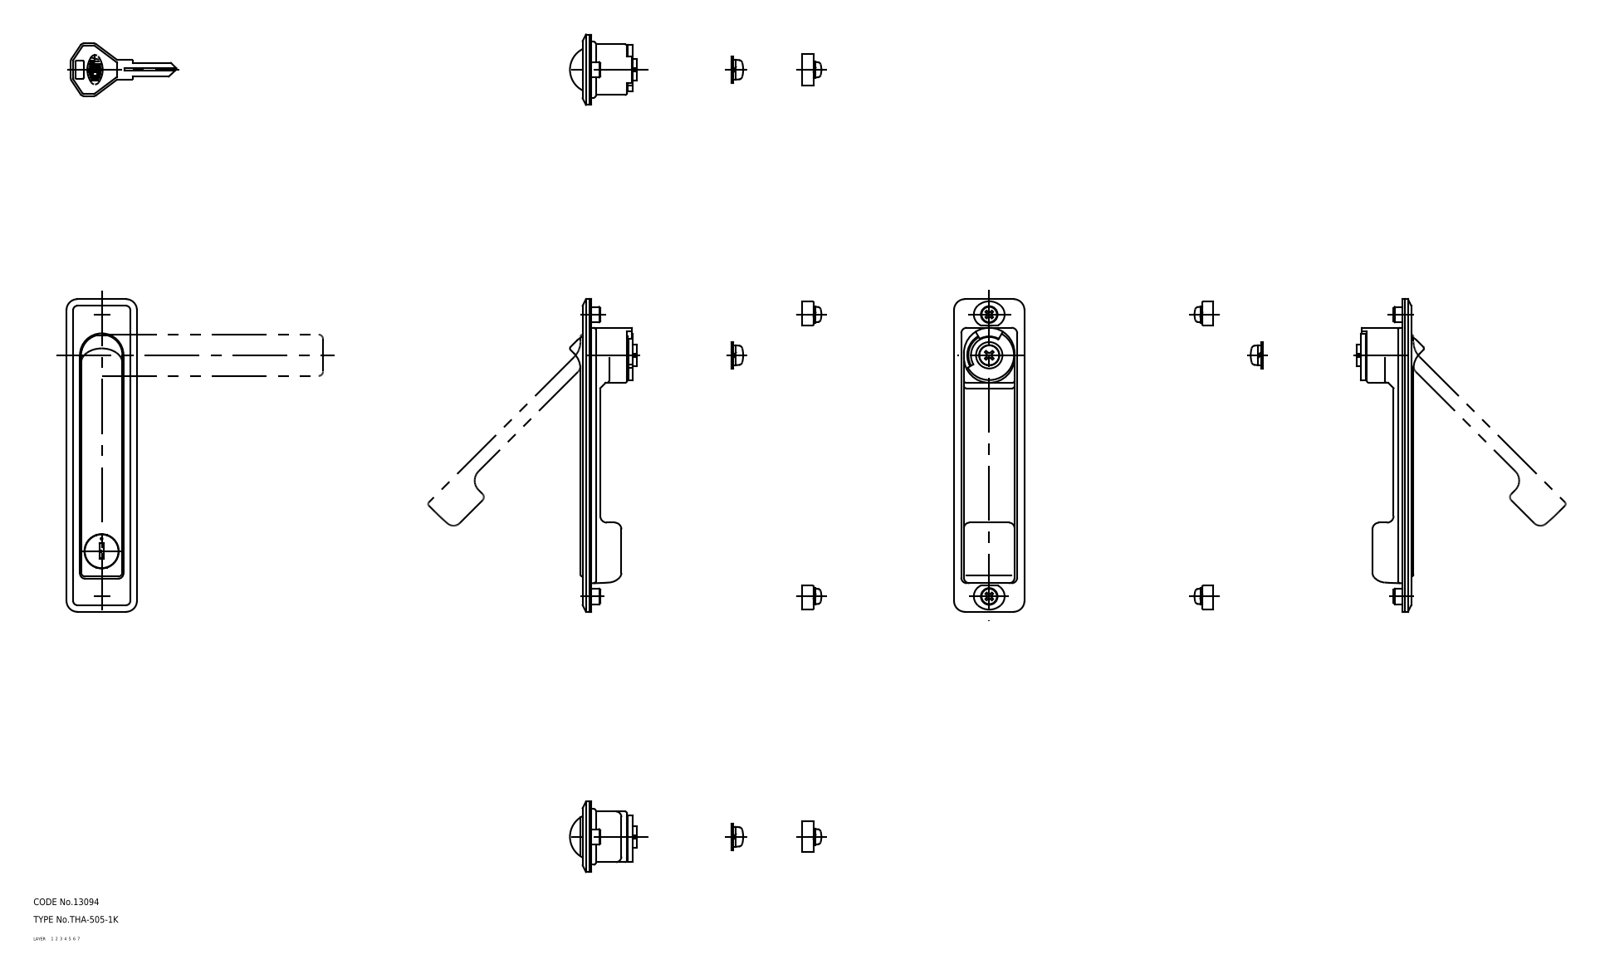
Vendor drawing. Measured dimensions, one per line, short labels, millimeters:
name: lock; key; bracket; screw_B (+8 more)
written by: CADfix (AUTOMOTIVE_DESIGN)
unit: mm
bodies: 13 solids, 444 faces (0 planar, 0 cylindrical, 444 other)
size: 142 × 93.93 × 32
volume: 39 562 mm³; area: 33 119 mm²
